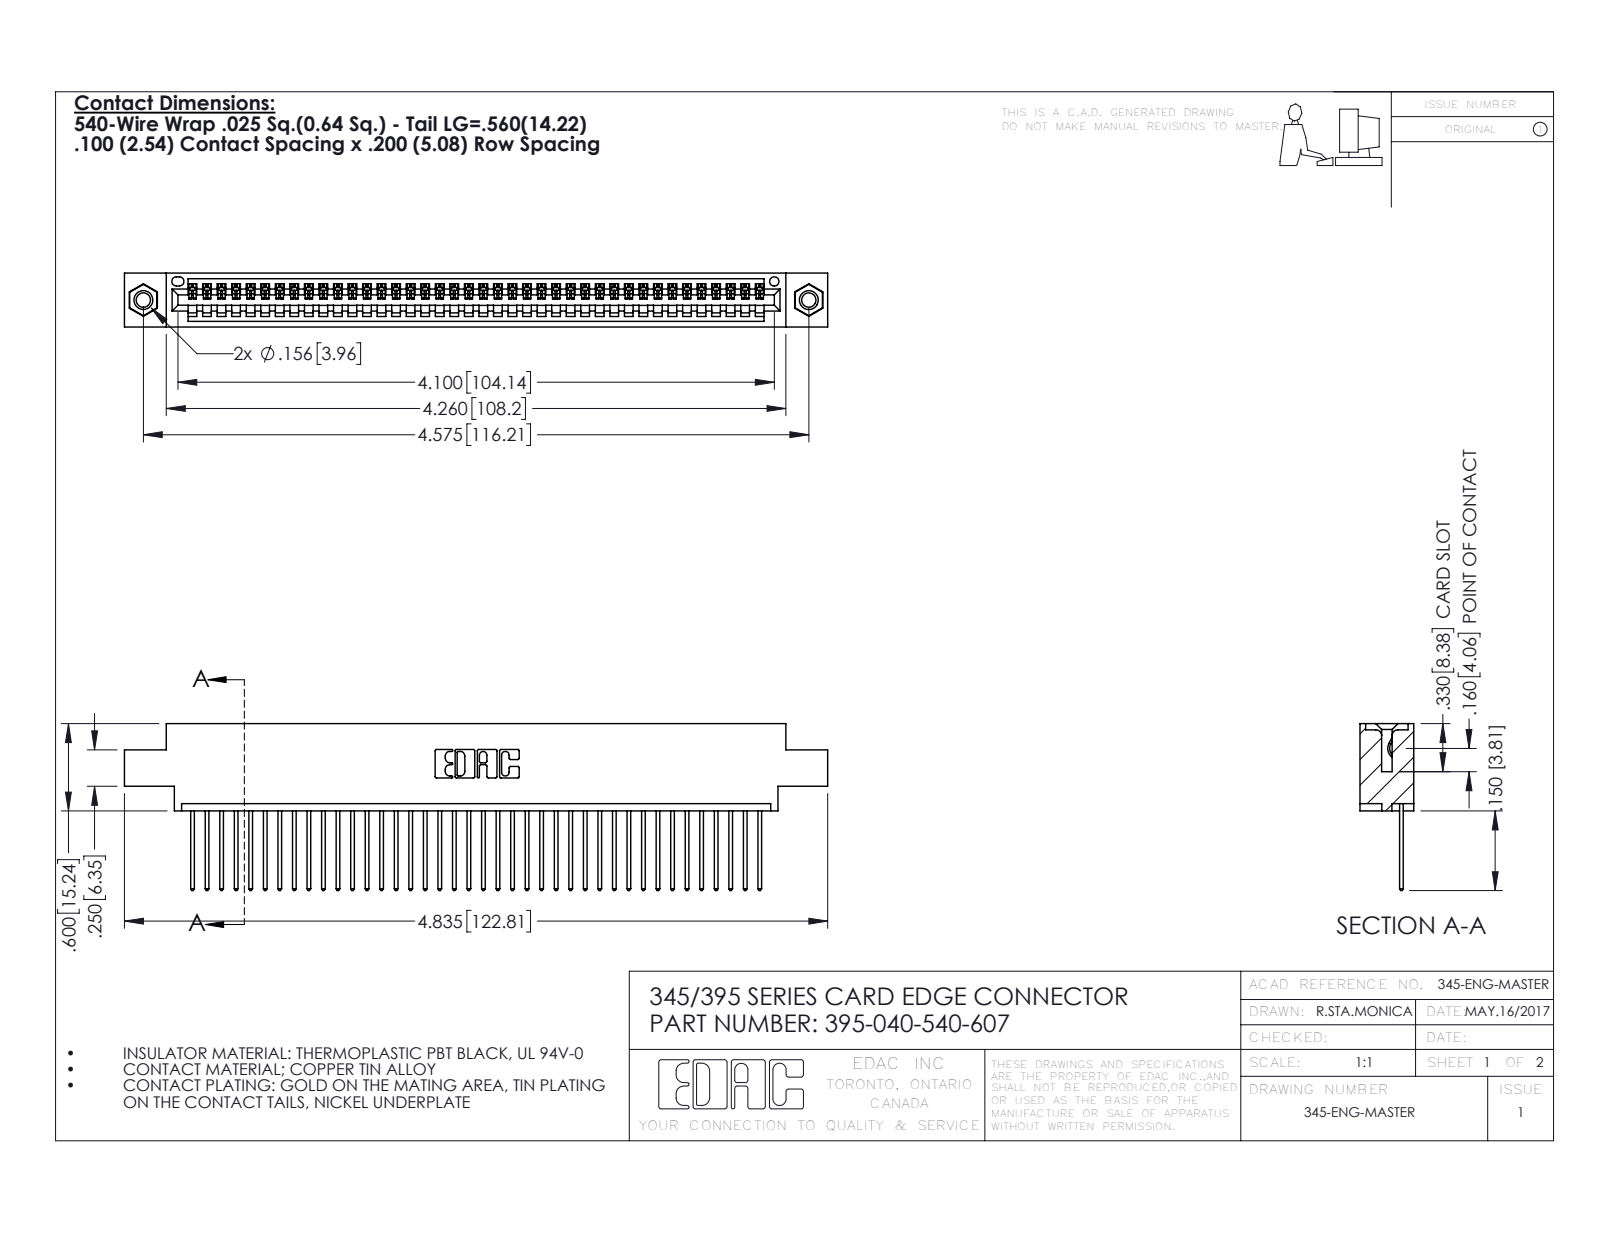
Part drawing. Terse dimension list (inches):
name: 345-292-001_345-293-140; 345 Part_0.170 Offset - 0.156 Dia-TI; 395-040-540-607; 345-250-001_345-250-005-103
written by: SolidWorks 2016 (CONFIG_CONTROL_DESIGN)
unit: in
bodies: 43 solids, 2510 faces (1716 planar, 778 cylindrical, 16 other)
size: 4.835 × 1.147 × 0.37
volume: 0.706 in³; area: 24.65 in²
holes: 2× ⌀0.098, 2× ⌀0.125, 2× ⌀0.156, 1× ⌀0.064
bosses: 2× ⌀0.155
rounds: 80× R0.006, 80× R0.01, 22× R0.01, 6× R0.007, 6× R0.031, 3× R0.026, 2× R0.031, 2× R0.04
face distances: 0.072, 0.298, 0.37, 0.098, 0.272, 0.025, 0.2, 0.225, 0.175, 0.149
hole spacings: 0.27, 4.339, 4.575
